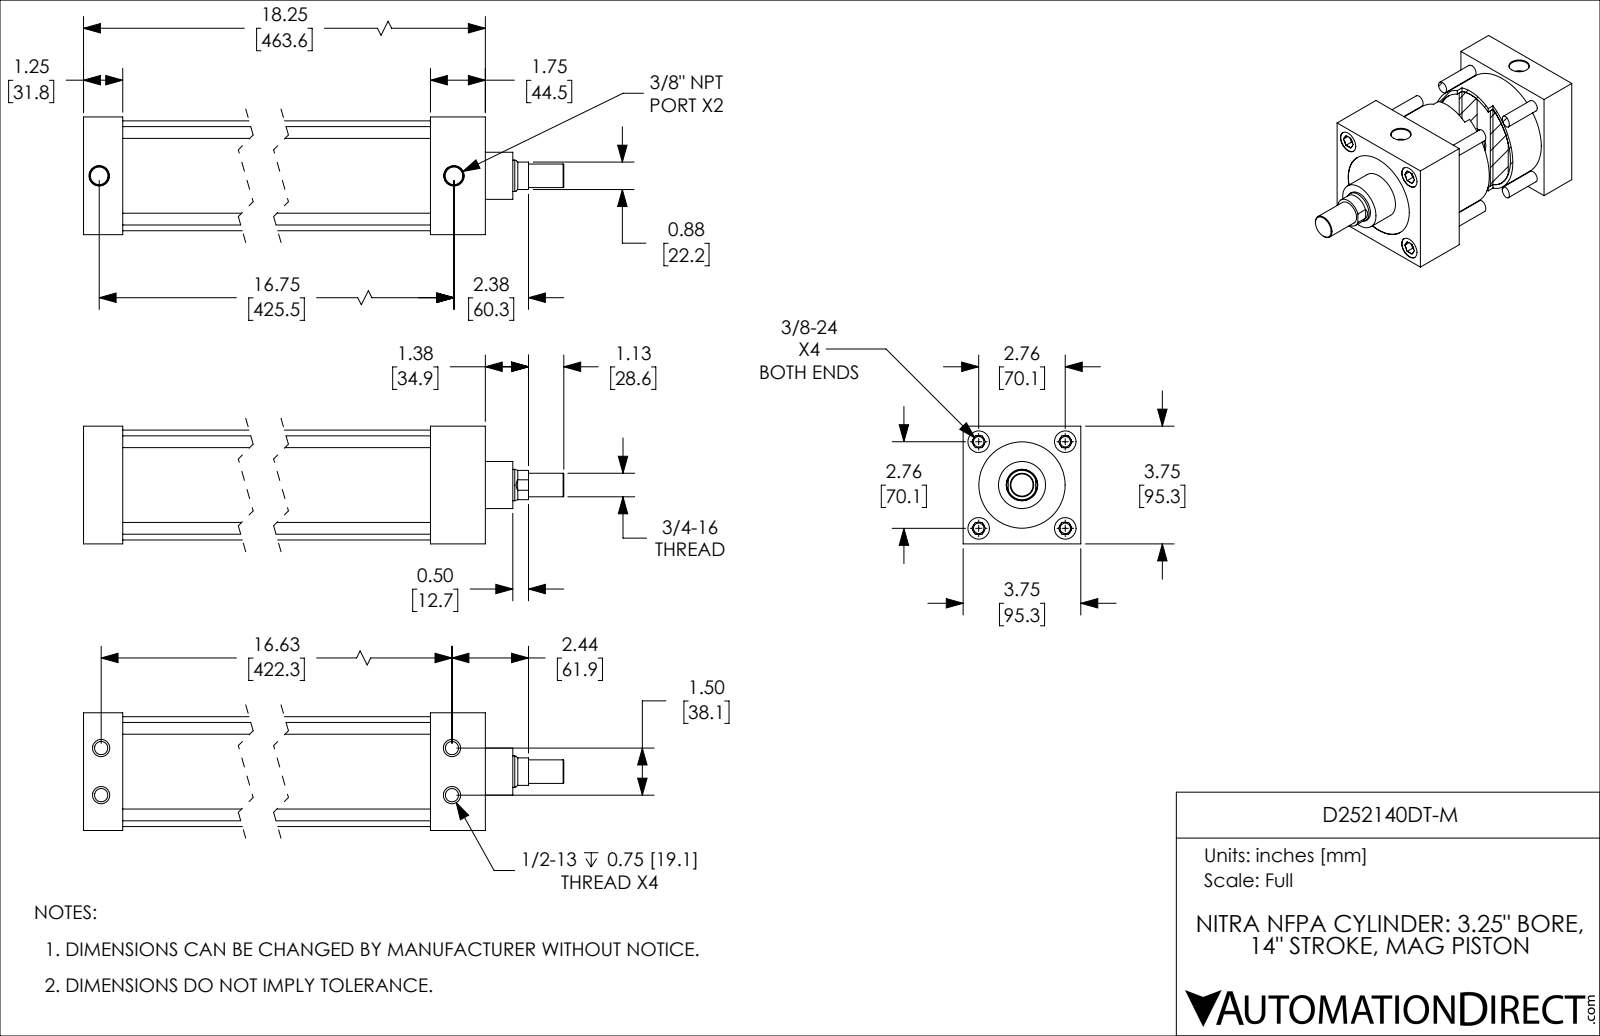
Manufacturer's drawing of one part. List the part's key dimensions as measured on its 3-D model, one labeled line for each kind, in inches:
Part name (STEP PRODUCT): D252140DT-M_BODY; D252140DT-M_PISTON_KK1; D252140DT-M
STEP written by: SolidWorks 2019 (CONFIG_CONTROL_DESIGN)
Units: inches
Bodies: 2 solids, 198 faces (58 planar, 62 cylindrical, 78 other)
Overall size (bounding box): 20.75 × 3.75 × 3.75
Volume: 90.66 in³ · Surface area: 608.2 in²
Round holes (diameter × count): ⌀0.332 ×4, ⌀0.422 ×4, ⌀0.687 ×4, ⌀0.562 ×2, ⌀1 ×1, ⌀2.75 ×1, ⌀3.251 ×1
Round bosses / shafts (diameter × count): ⌀0.375 ×4, ⌀3.501 ×1, ⌀3.249 ×1, ⌀1.5 ×1, ⌀0.999 ×1, ⌀0.75 ×1
Partial cylindrical surfaces — rounded edges, fillets, slot ends (radius × count): R0.469 ×1
Main face-to-face distances: 1.25, 3.75, 16.5, 15.25, 2.5, 14, 18.25, 17, 15.75, 1.75
Hole centre spacings: 0.753, 1.952, 2.76, 16.704, 1.5, 3.903, 16.625, 16.693
